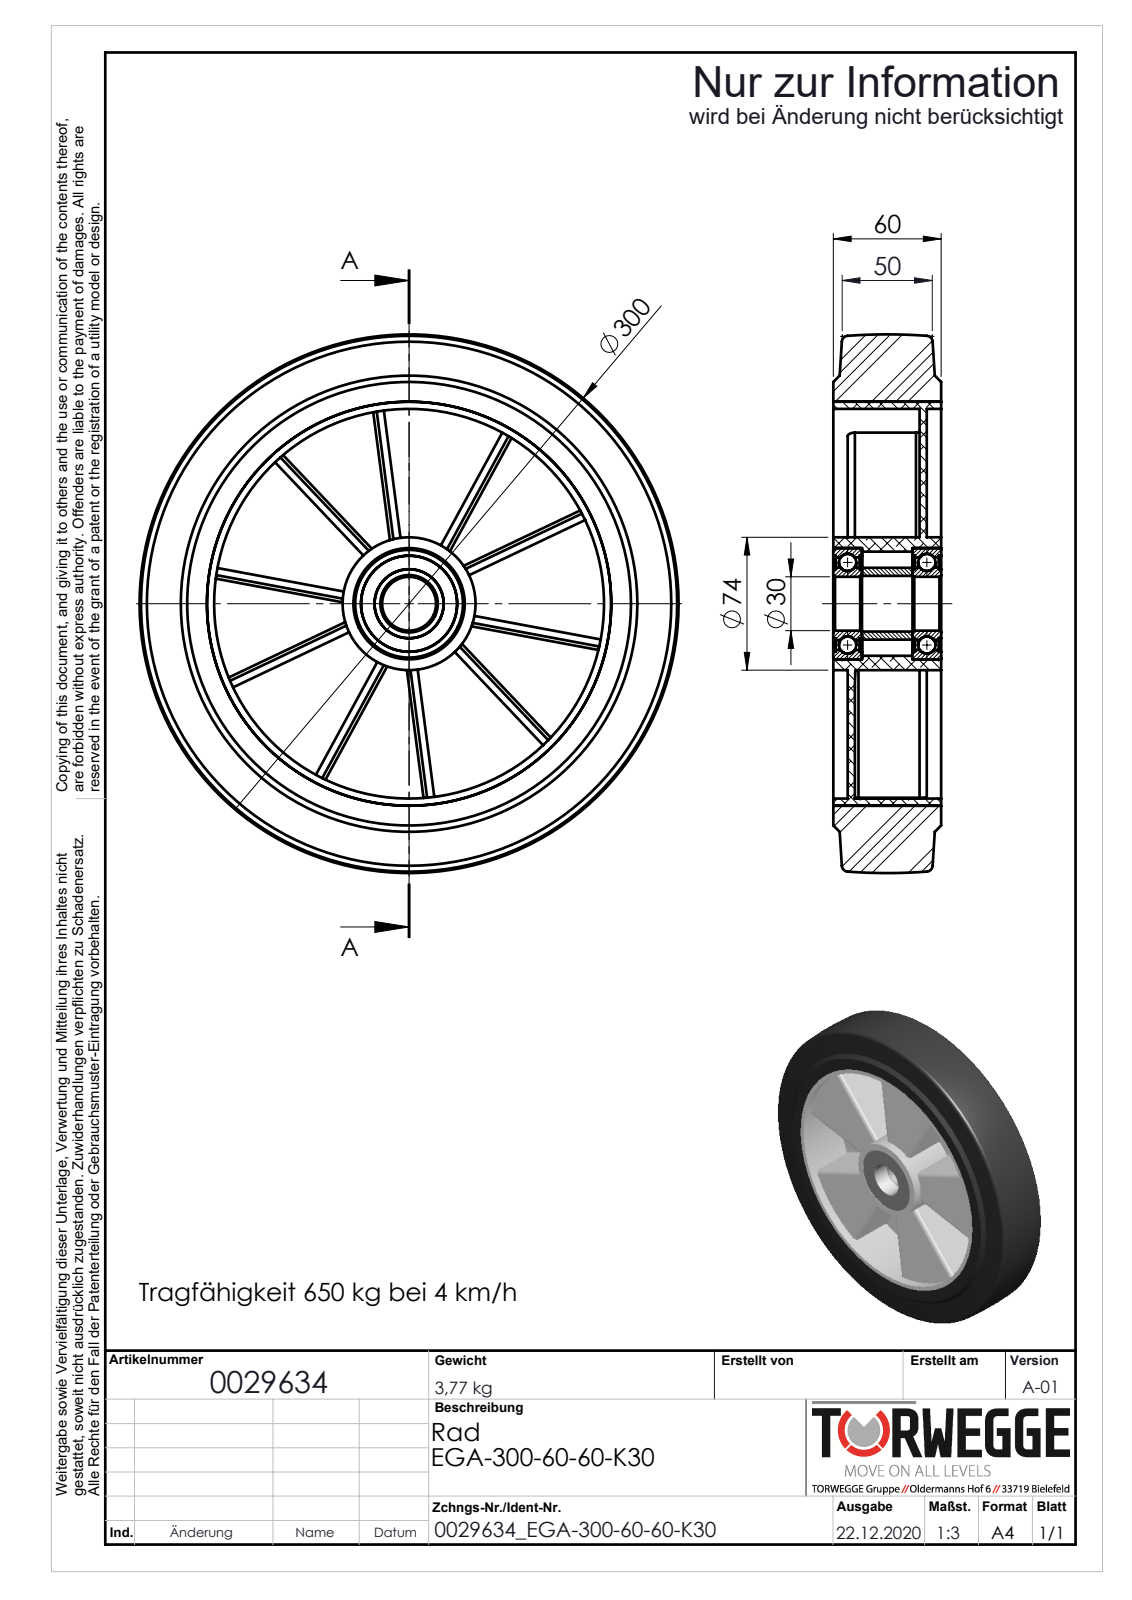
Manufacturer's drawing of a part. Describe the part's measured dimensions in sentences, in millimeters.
The part is named "0029634". Its 3-D file was written by "SolidWorks 2018 (AUTOMOTIVE_DESIGN)". It is 13 solids with 242 faces: 74 planar, 118 cylindrical and 50 other. Overall it measures 300 by 300 by 60.1 millimeters. Its volume is 2 228 000 cubic millimeters and its surface area 429 798 square millimeters. Round holes: 1 of diameter 30, 1 of diameter 31, 1 of diameter 38.48, 1 of diameter 51.57, 1 of diameter 53.52, 1 of diameter 58, 1 of diameter 62, 1 of diameter 217, 1 of diameter 225. Round bosses or shafts: 1 of diameter 74, 1 of diameter 40.43, 1 of diameter 40. Partial cylindrical surfaces (rounded edges, fillets, slot ends): 18 of radius 2, 15 of radius 4. The main face-to-face distances are 4, 40, 8, 52, 12, 48, 44, 36, 60, 3.95.
